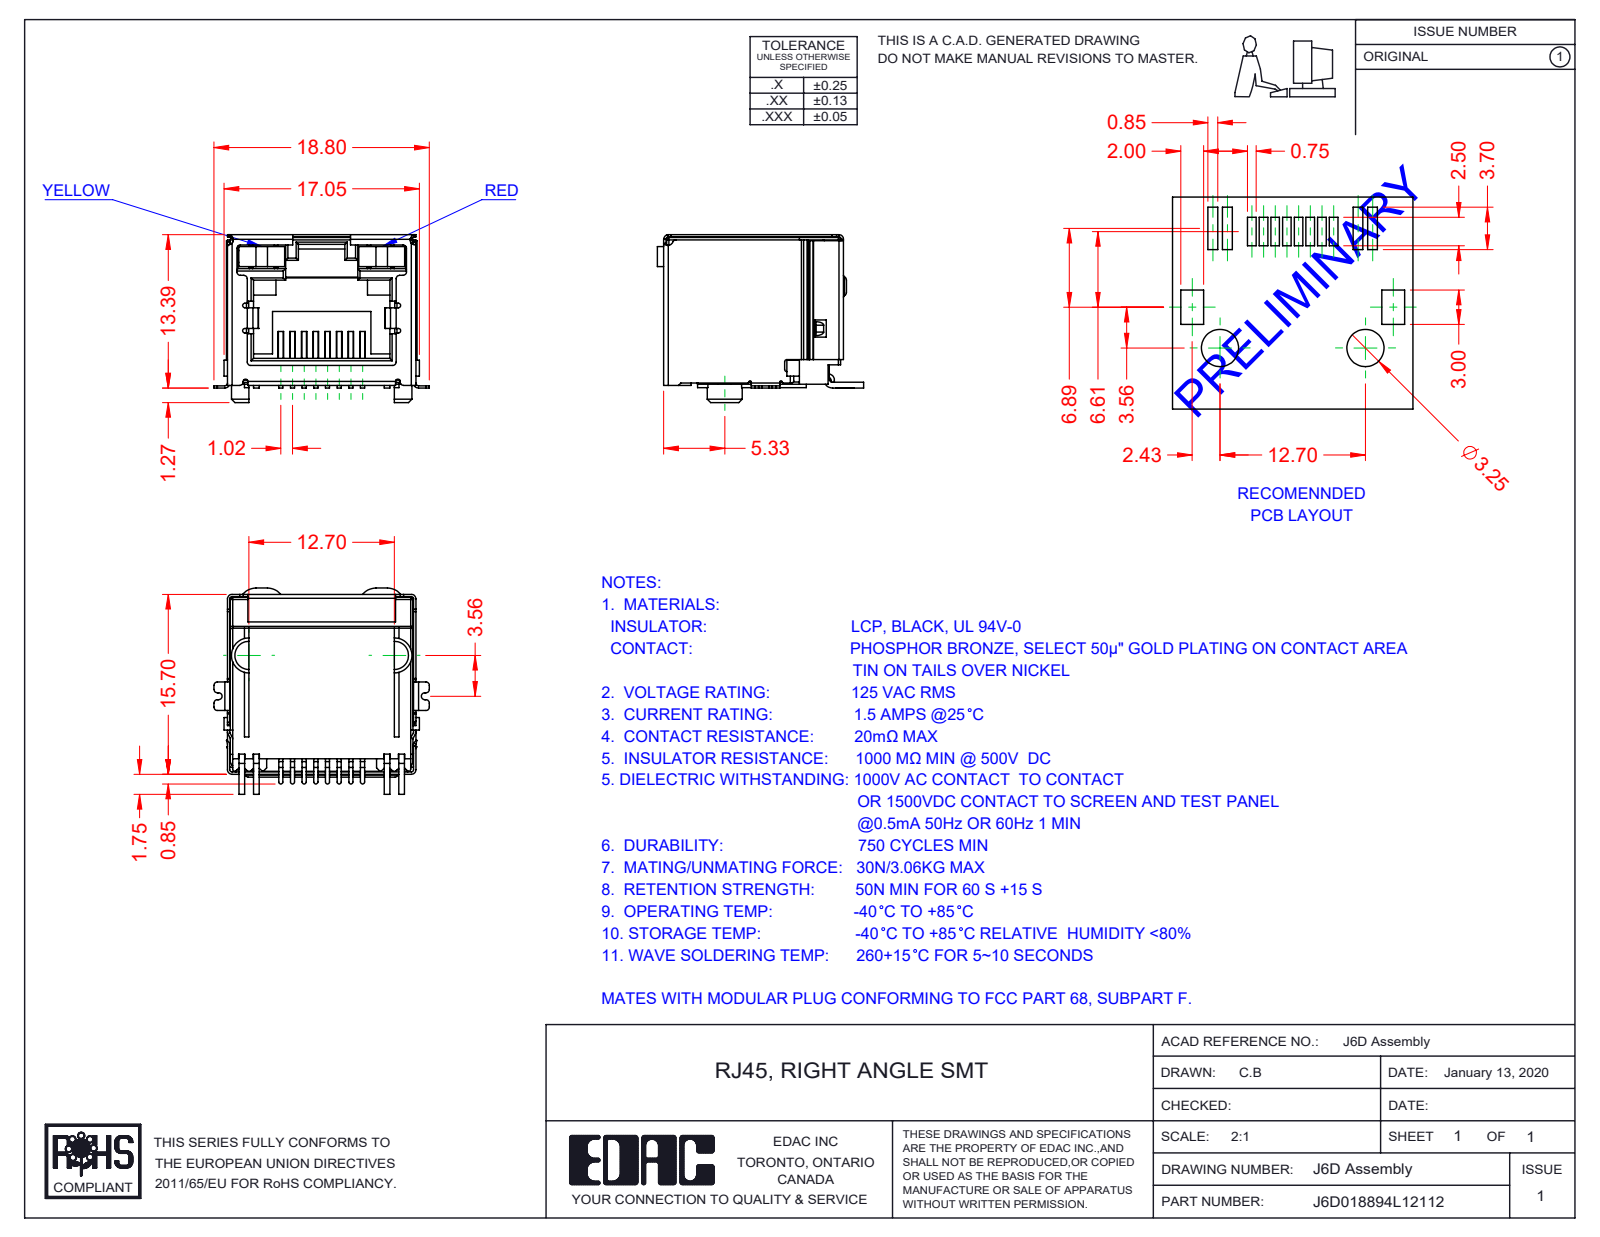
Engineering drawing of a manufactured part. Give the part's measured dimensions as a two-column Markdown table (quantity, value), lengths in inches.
| quantity | value |
| --- | --- |
| part name | 6D LED LH_1-Yellow; 6D Contacts; 6D Insulator; 6D Shield_LED - No EMI (+2 more) |
| STEP written by | SolidWorks 2016 (CONFIG_CONTROL_DESIGN) |
| units | inches |
| bodies | 12 solids, 893 faces (644 planar, 216 cylindrical, 33 other) |
| overall size | 0.74 × 0.709 × 0.577 |
| volume | 0.11 in³ |
| surface area | 7.592 in² |
| partial cylindrical surfaces (radius × count) | 0.012 × 39, 0.008 × 37, 0.016 × 16, 0.004 × 12, 0.006 × 8, 0.007 × 8, 0.02 × 6, 0.059 × 5 |
| main face-to-face distances | 0.63, 0.64, 0.638, 0.089, 0.039, 0.628, 0.632, 0.504, 0.018, 0.648 |
